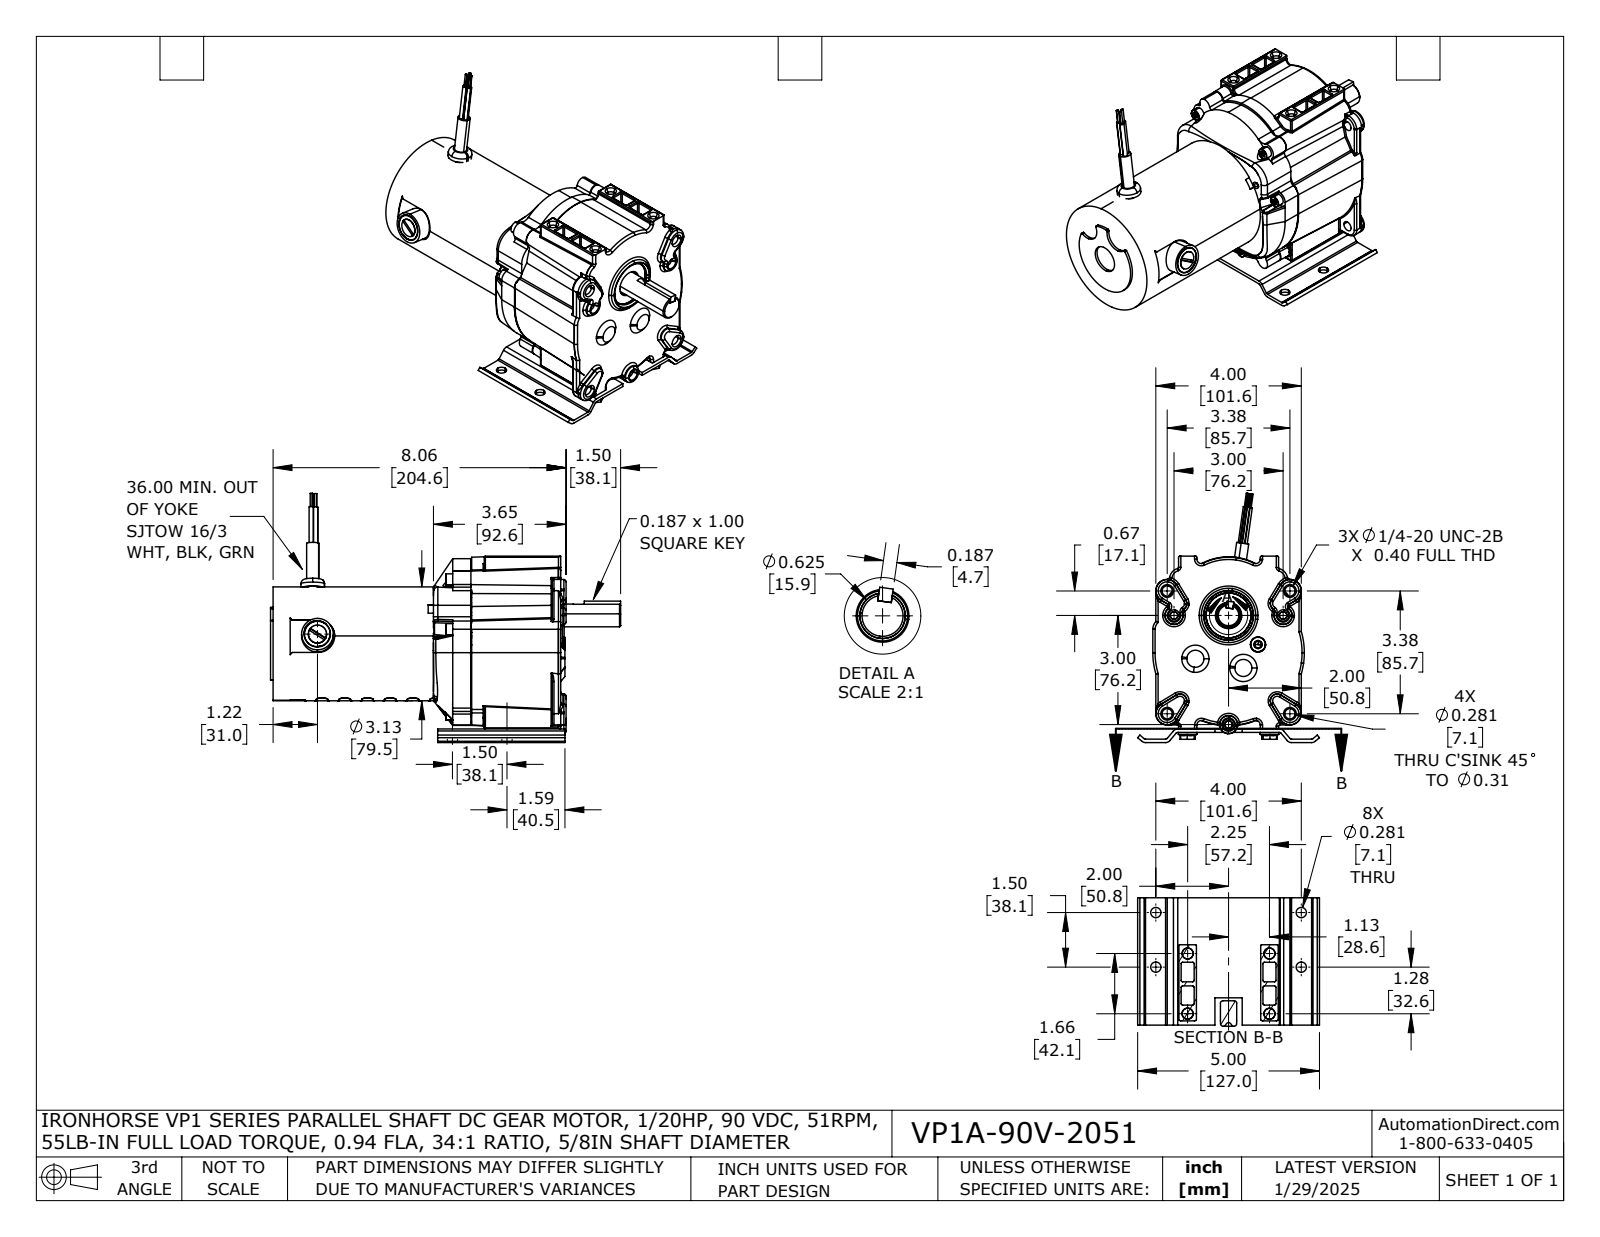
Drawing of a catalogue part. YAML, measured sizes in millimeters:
part_name: "VP1A-90V-2051"
step_written_by: "SolidWorks 2024 (AUTOMOTIVE_DESIGN)"
units: millimeters
bodies: {solids: 8, faces: 2435, planar: 642, cylindrical: 688, other: 1105}
overall_size: [244.5, 174.1, 127]
volume: 1351000
surface_area: 196100
round_holes:
  - {diameter: 7.1, count: 12}
  - {diameter: 5.5, count: 5}
  - {diameter: 5.3, count: 3}
  - {diameter: 3.4, count: 2}
  - {diameter: 4, count: 2}
  - {diameter: 4.2, count: 2}
  - {diameter: 5.2, count: 2}
  - {diameter: 10.1, count: 2}
  - {diameter: 17.5, count: 2}
  - {diameter: 19.1, count: 1}
  - {diameter: 20.7, count: 1}
  - {diameter: 22.2, count: 1}
round_bosses_or_shafts:
  - {diameter: 7.8, count: 5}
  - {diameter: 4.8, count: 5}
  - {diameter: 13, count: 4}
  - {diameter: 7.6, count: 4}
  - {diameter: 3, count: 3}
  - {diameter: 1.5, count: 3}
  - {diameter: 22.2, count: 2}
  - {diameter: 18.6, count: 2}
partial_cylinders:
  - {radius: 0.8, count: 52}
  - {radius: 0.8, count: 38}
  - {radius: 1.6, count: 22}
  - {radius: 3, count: 18}
  - {radius: 4, count: 13}
  - {radius: 4.8, count: 10}
  - {radius: 1.3, count: 8}
  - {radius: 1.5, count: 7}
face_to_face_distances: [62.2, 88.9, 26.7, 2.4, 2.4, 200.9, 138.7, 112, 3.3, 7.1]
hole_center_spacings: [38.1, 43, 17.7, 24.2, 31.1, 36.2, 39.4, 42.1]
